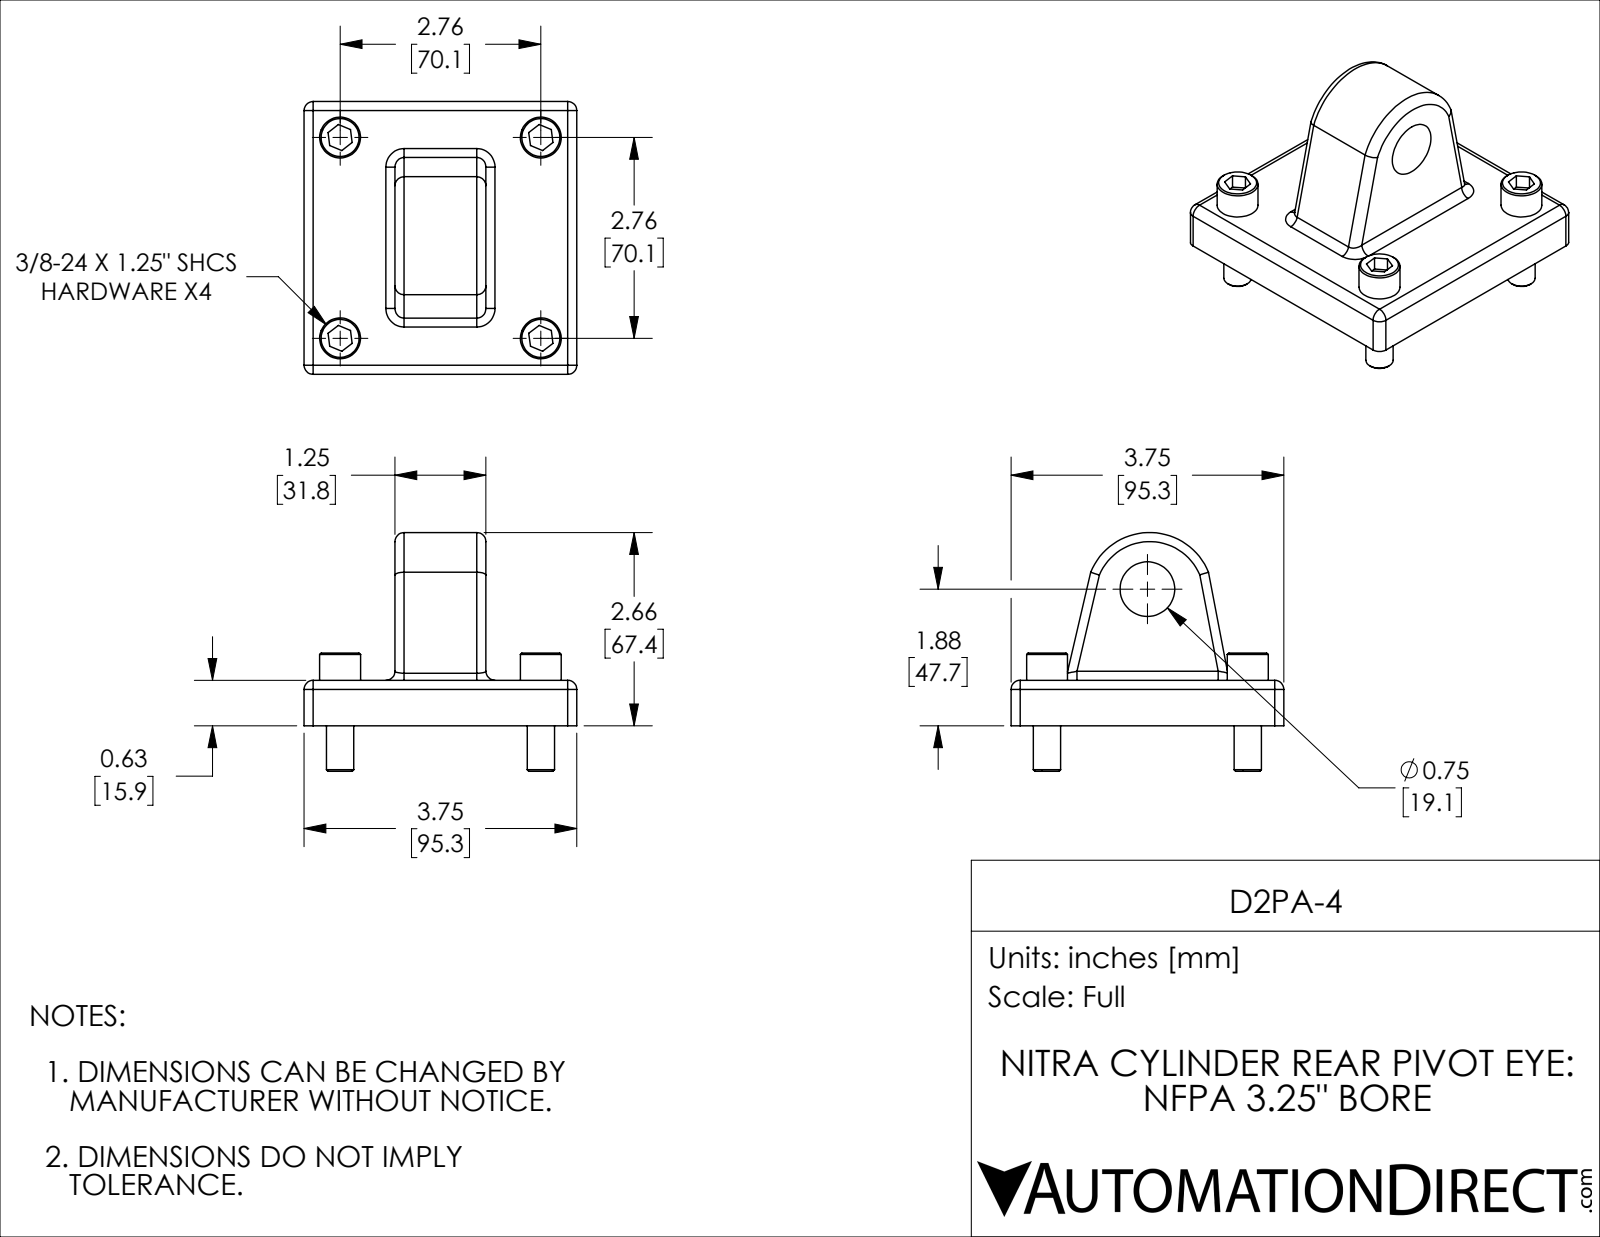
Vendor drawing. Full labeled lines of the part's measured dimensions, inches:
Part name (STEP PRODUCT): D2PA-4
STEP written by: SolidWorks 2019 (CONFIG_CONTROL_DESIGN)
Units: inches
Bodies: 5 solids, 120 faces (50 planar, 43 cylindrical, 27 other)
Overall size (bounding box): 3.75 × 3.75 × 3.28
Volume: 13.09 in³ · Surface area: 61.71 in²
Round holes (diameter × count): ⌀0.406 ×4, ⌀0.751 ×1
Round bosses / shafts (diameter × count): ⌀0.562 ×4, ⌀0.375 ×4
Partial cylindrical surfaces — rounded edges, fillets, slot ends (radius × count): R0.125 ×16, R0.875 ×1
Main face-to-face distances: 0.625, 1.25, 2.5, 3.75, 3.75, 0.375, 1, 1.625, 0.625, 0.188
Hole centre spacings: 2.76, 2.76, 3.903
